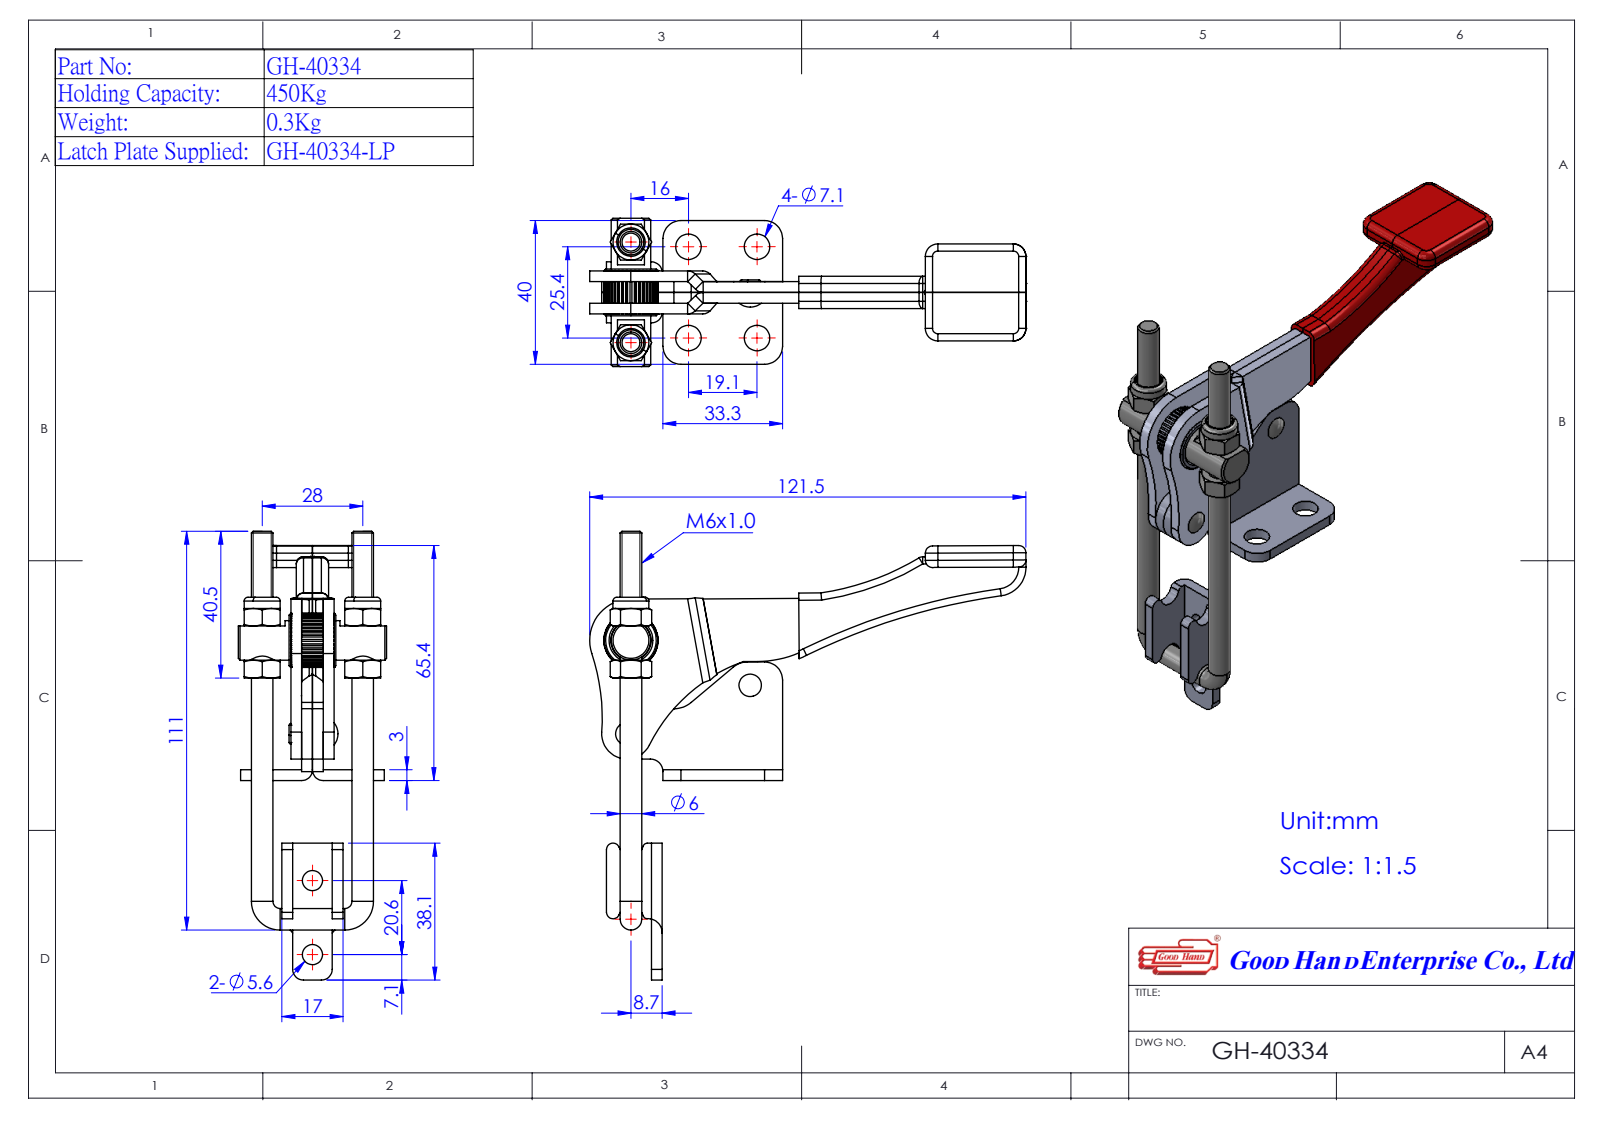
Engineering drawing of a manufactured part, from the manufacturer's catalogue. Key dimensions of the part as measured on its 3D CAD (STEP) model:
Part name (STEP PRODUCT): Group3^EMC40334; Group4^EMC40334; EMC40334; Group2^EMC40334
STEP written by: SolidWorks 2016 (AUTOMOTIVE_DESIGN)
Units: millimetres
Bodies: 4 solids, 320 faces (113 planar, 118 cylindrical, 89 other)
Overall size (bounding box): 125.11 × 121.55 × 41.3
Volume: 44 176 mm³ · Surface area: 25 560 mm²
Round holes (diameter × count): ⌀7.1 ×4, ⌀5.6 ×2, ⌀4 ×1
Round bosses / shafts (diameter × count): ⌀6 ×3, ⌀10 ×2, ⌀11 ×1, ⌀4.8 ×1
Partial cylindrical surfaces — rounded edges, fillets, slot ends (radius × count): R3.5 ×7, R3.01 ×6, R5 ×5, R46.57 ×4, R1.18 ×2, R1.8 ×2, R3 ×2, R4 ×1
Main face-to-face distances: 3, 1.5, 6, 9, 10.5, 7.5, 11.5, 2.5, 14.5, 12
Hole centre spacings: 19.1, 25.4, 31.78, 20.6
